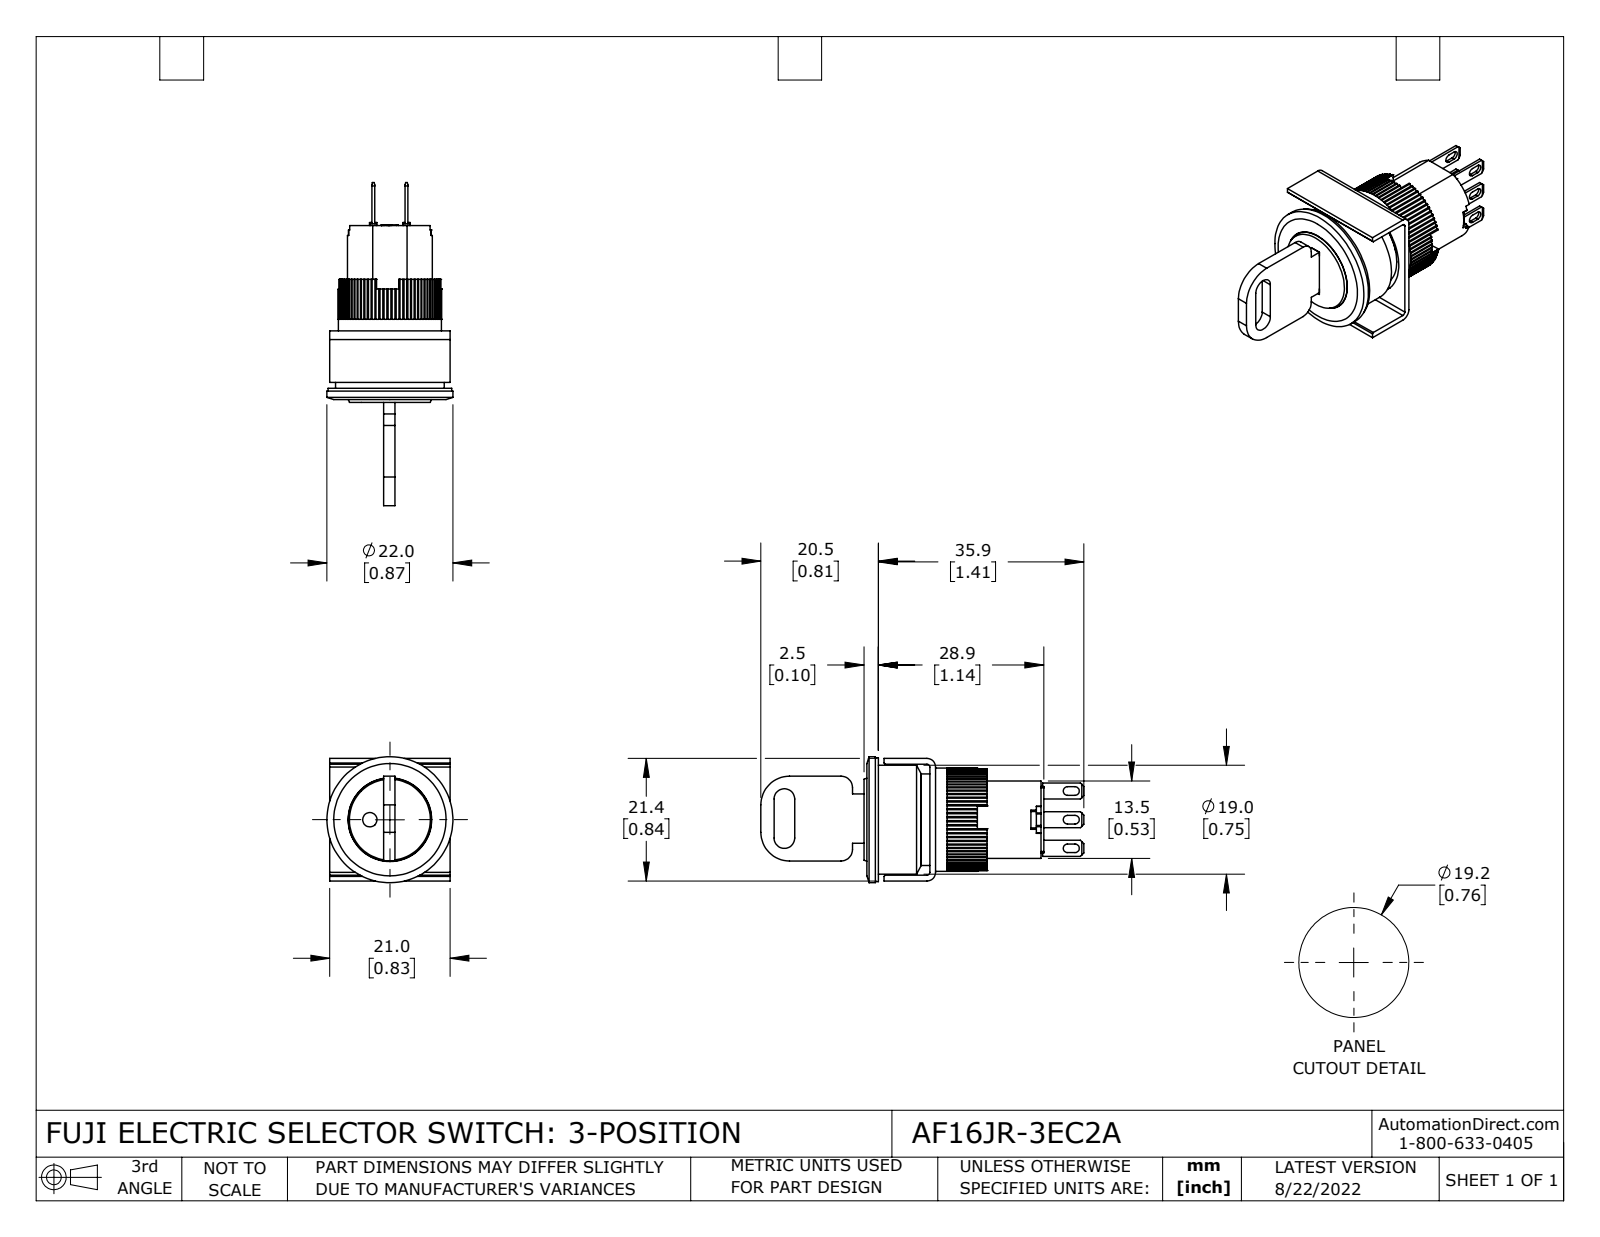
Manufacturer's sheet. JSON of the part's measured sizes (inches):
{"part_name": "AF16JR-3EC2A", "step_written_by": "SolidWorks 2021 (CONFIG_CONTROL_DESIGN)", "units": "inches", "bodies": {"solids": 13, "faces": 707, "planar": 518, "cylindrical": 183, "other": 6}, "overall_size": [2.22, 0.866, 0.866], "volume_in3": 0.495, "surface_area_in2": 11.24, "round_holes": [[0.039, 1], [0.098, 1], [0.575, 1], [0.709, 1], [0.748, 1]], "round_bosses_or_shafts": [[0.866, 1], [0.85, 1], [0.63, 1], [0.583, 1], [0.571, 1]], "partial_cylinders_radius": [[0.01, 80], [0.008, 12], [0.03, 6], [0.02, 2], [0.059, 2], [0.071, 2], [0.079, 2], [0.197, 2]], "face_to_face_distances": [0.079, 0.039, 0.02, 0.374, 0.177, 0.098, 0.394, 0.803, 0.059, 0.764], "hole_center_spacings": [0.138]}
